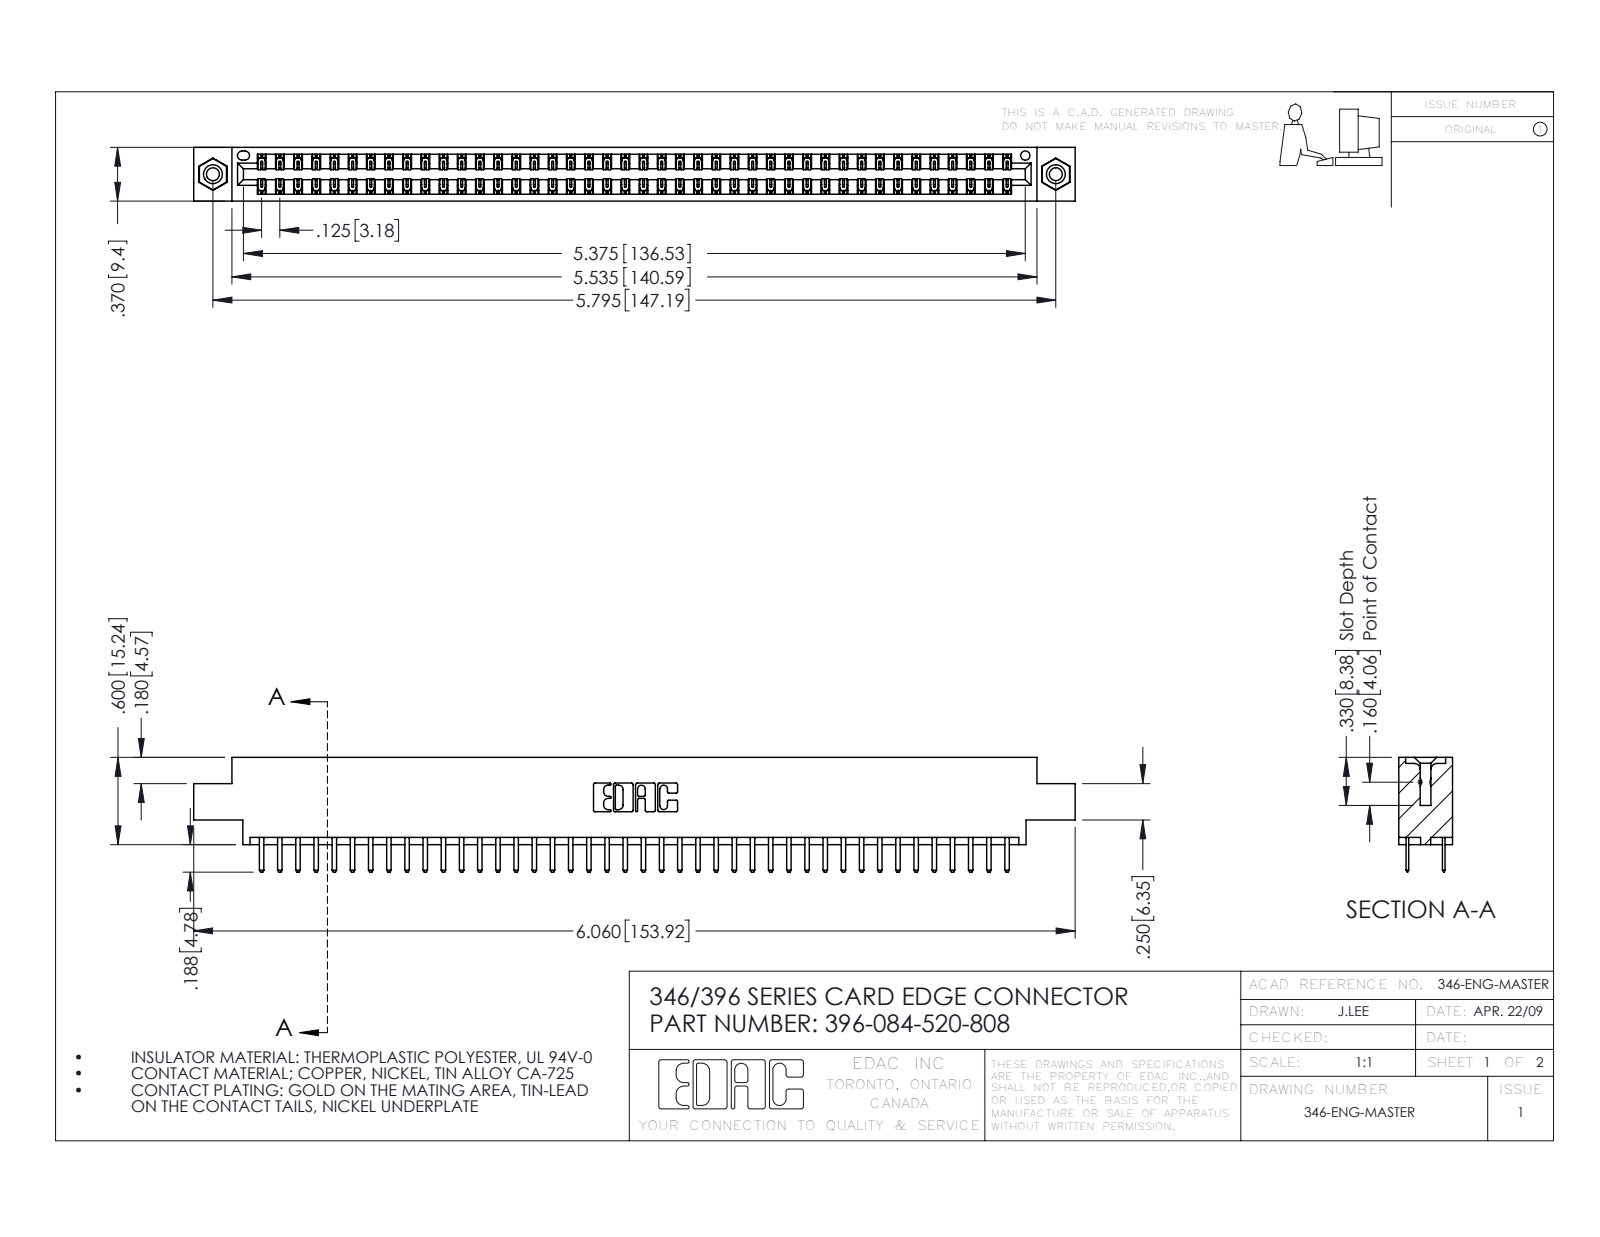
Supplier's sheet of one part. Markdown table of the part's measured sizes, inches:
| quantity | value |
| --- | --- |
| part name | 346 Part_0.170 Offset - 0.156 Dia-TI; 345-292-001_345-293-120; 396-084-520-808; 345-250-001_345-250-003-102 |
| STEP written by | SolidWorks 2016 (CONFIG_CONTROL_DESIGN) |
| units | inches |
| bodies | 87 solids, 4890 faces (3220 planar, 1654 cylindrical, 16 other) |
| overall size | 6.06 × 0.788 × 0.37 |
| volume | 0.904 in³ |
| surface area | 31.73 in² |
| round holes (diameter × count) | 0.089 × 2, 0.125 × 2, 0.156 × 2, 0.064 × 1 |
| round bosses / shafts (diameter × count) | 0.155 × 2 |
| partial cylindrical surfaces (radius × count) | 0.006 × 126, 0.01 × 88, 0.01 × 22, 0.007 × 6, 0.031 × 6, 0.026 × 3, 0.014 × 2, 0.022 × 2 |
| main face-to-face distances | 0.048, 0.322, 0.25, 0.37, 0.275, 0.072, 0.298, 0.025, 0.222, 0.148 |
| hole center spacings | 0.246, 5.586, 5.795 |
